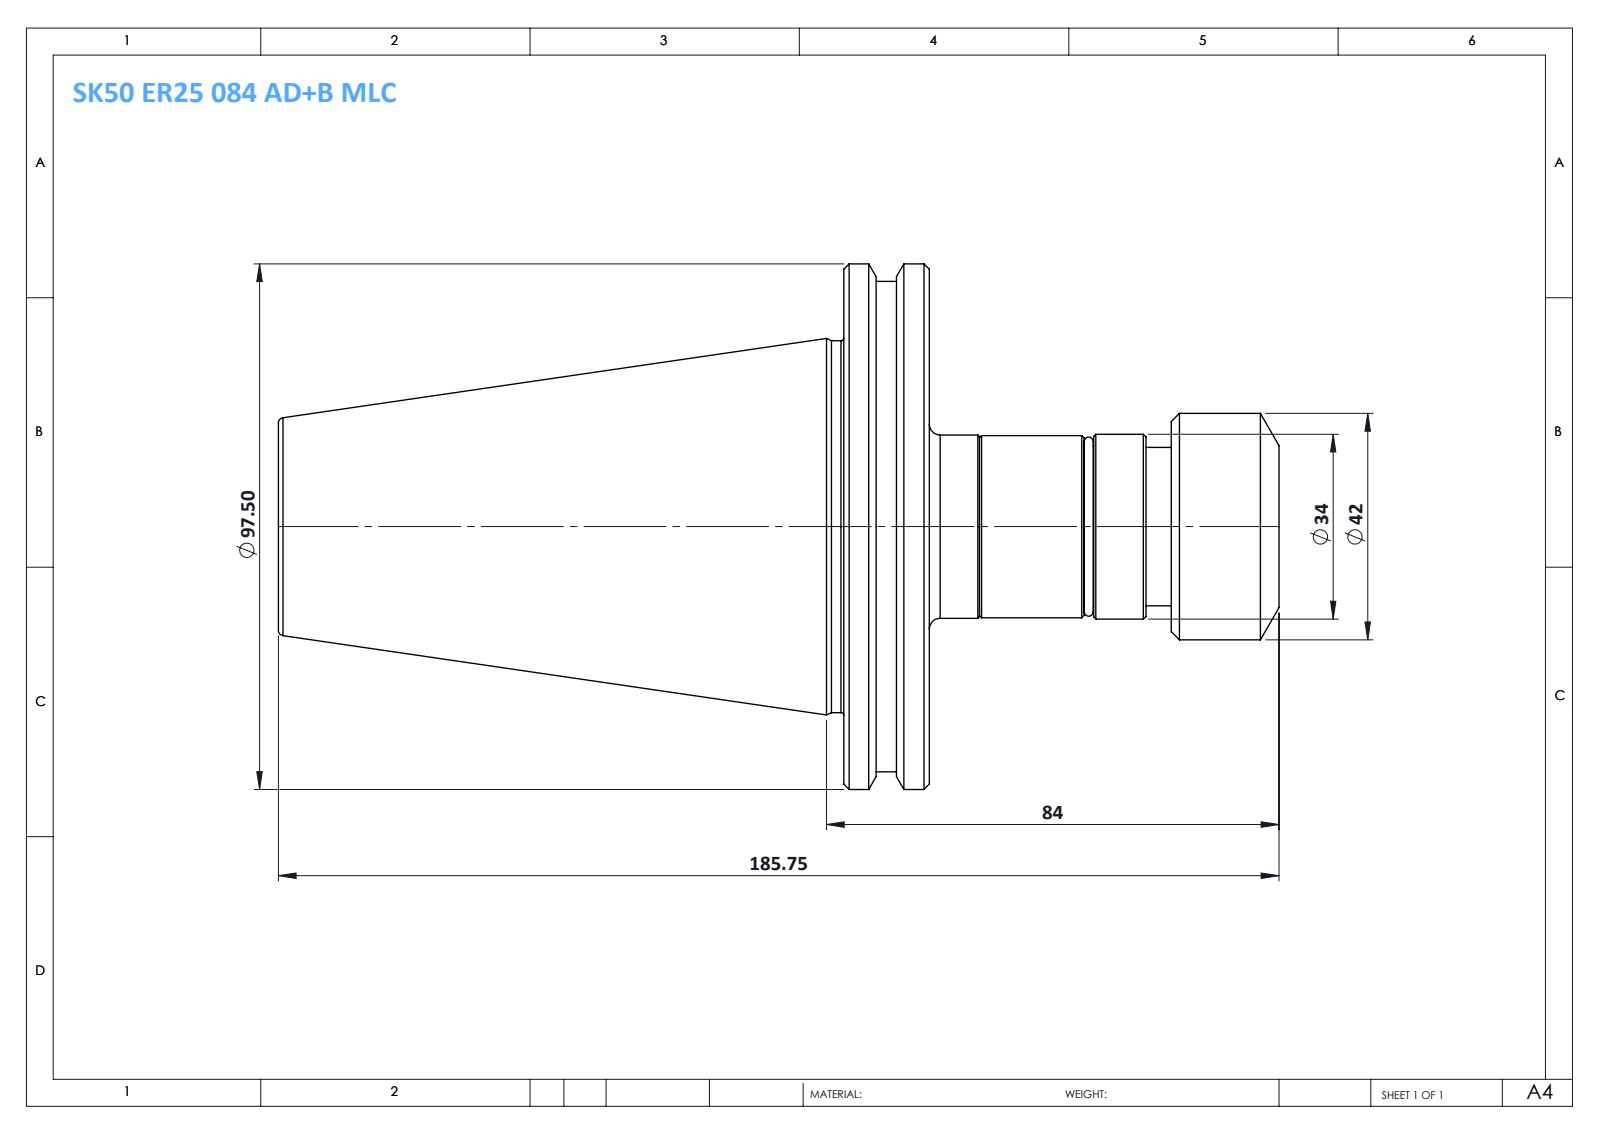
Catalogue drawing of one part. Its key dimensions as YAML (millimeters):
part_name: "SK 50 ER 25 084 AD+B MLC (1)"
step_written_by: "SolidWorks 2014 (CONFIG_CONTROL_DESIGN)"
units: millimeters
bodies: {solids: 2, faces: 67, planar: 11, cylindrical: 20, other: 36}
overall_size: [185.75, 97.5, 97.5]
volume: 439400
surface_area: 45708
round_bosses_or_shafts:
  - {diameter: 97.5, count: 1}
  - {diameter: 91, count: 1}
  - {diameter: 69, count: 1}
  - {diameter: 42, count: 1}
  - {diameter: 34.3, count: 1}
  - {diameter: 34, count: 1}
  - {diameter: 33.8, count: 1}
  - {diameter: 29.9, count: 1}
face_to_face_distances: [15.9, 120.85, 104.95, 64.9, 80.8, 185.75, 20, 44.9, 60.8, 165.75]
